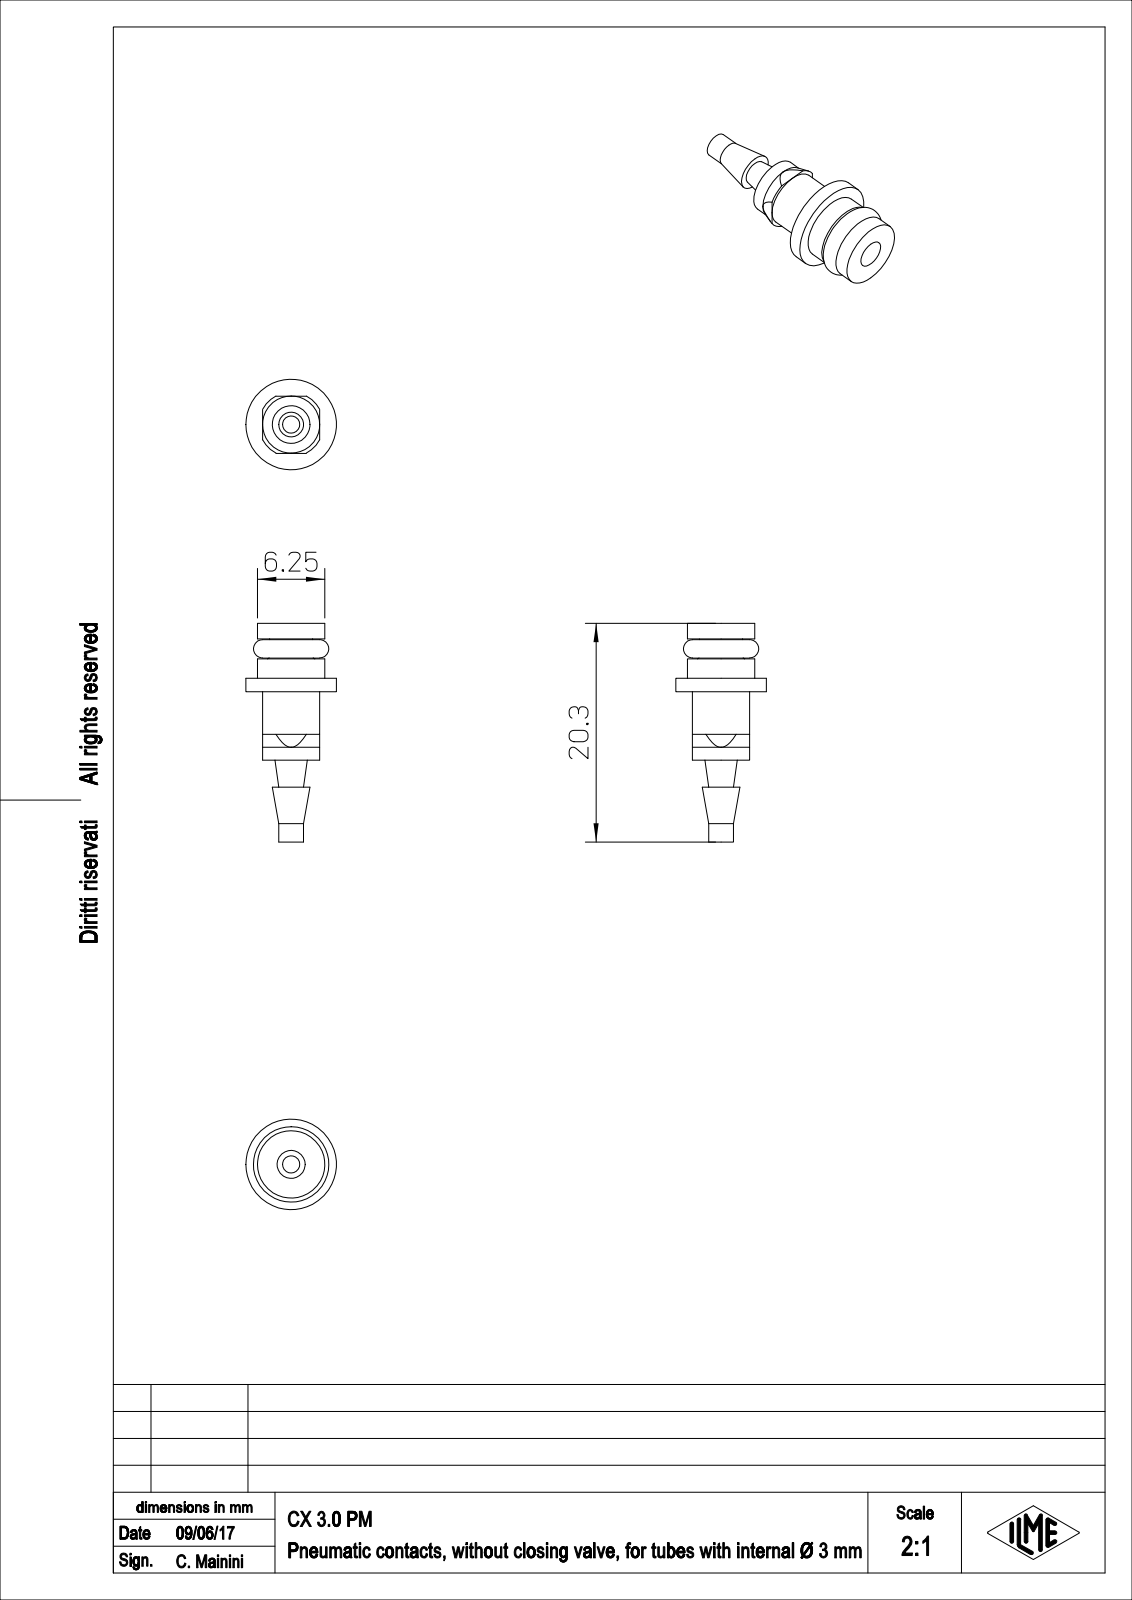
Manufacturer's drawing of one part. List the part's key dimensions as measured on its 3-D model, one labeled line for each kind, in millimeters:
Part name (STEP PRODUCT): CX_3.0_PM
STEP written by: PTC Creo Elements/Direct Modeling 19.0E 27-Jun-2016 (C) Parametric Technology GmbH (AUTOMOTIVE_DESIGN)
Units: millimetres
Bodies: 1 solid, 51 faces (17 planar, 20 cylindrical, 14 other)
Overall size (bounding box): 20.3 × 8.4 × 8.4
Volume: 335 mm³ · Surface area: 640 mm²
Round holes (diameter × count): ⌀1.6 ×1, ⌀2.6 ×1
Round bosses / shafts (diameter × count): ⌀8.4 ×1, ⌀6.25 ×1, ⌀5.3 ×1, ⌀4 ×1, ⌀2.3 ×1
Main face-to-face distances: 6.35, 5.1, 1.25, 4.9, 3.65, 1.45, 7.6, 3.05, 1.8, 1.85
